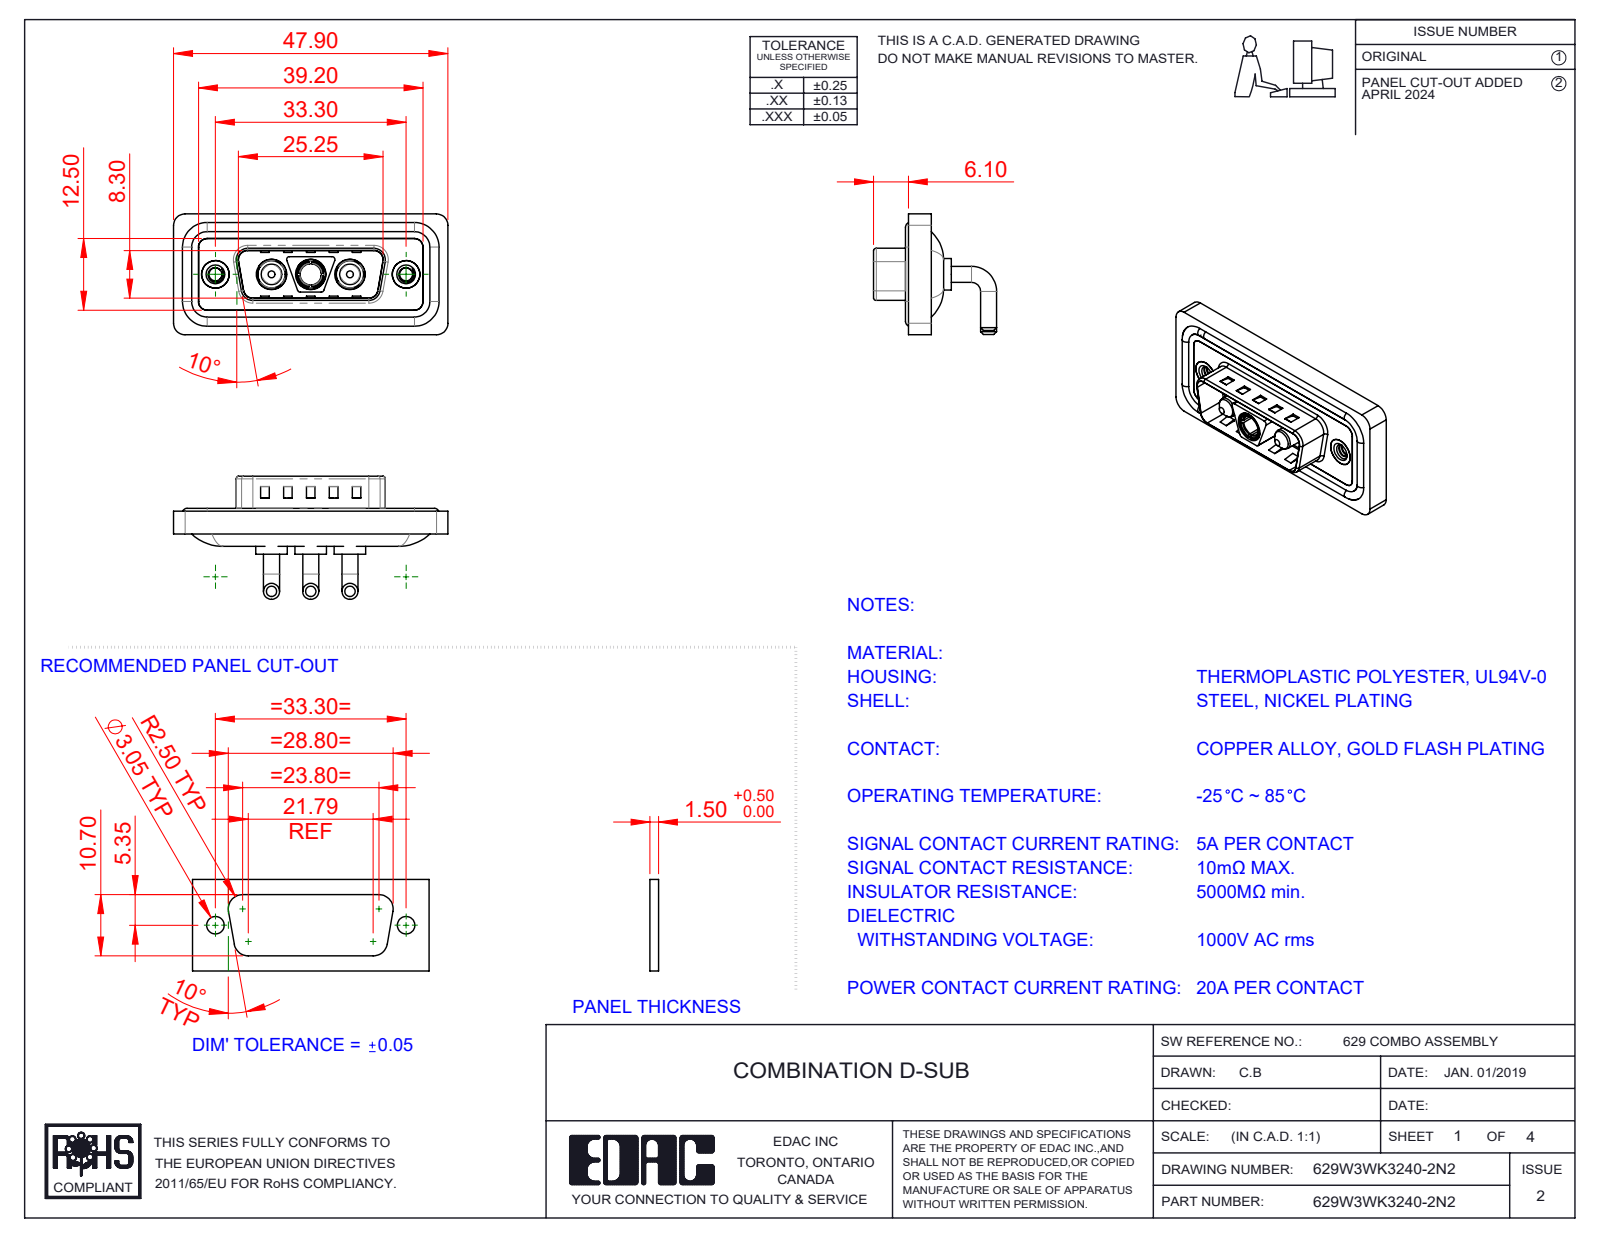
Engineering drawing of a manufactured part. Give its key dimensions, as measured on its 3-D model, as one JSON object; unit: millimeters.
{"part_name": "629Combo Waterproof Housing_15 Contacts; Power Pin_20A RA; 629Combo Threaded Rivet_2; Power Socket_20A RA (+4 more)", "step_written_by": "SolidWorks 2023 (CONFIG_CONTROL_DESIGN)", "units": "millimeters", "bodies": {"solids": 13, "faces": 621, "planar": 231, "cylindrical": 256, "other": 134}, "overall_size": [47.9, 21.5, 21.1], "volume_mm3": 5896, "surface_area_mm2": 9416, "round_holes": [[4.85, 3], [5.3, 3], [2.26, 2], [4, 2], [4.8, 2], [5, 2], [3.7, 1]], "round_bosses_or_shafts": [[2.8, 6], [1.6, 4], [5.5, 3], [5.2, 3], [4.75, 3], [3.75, 3], [4.9, 2], [3.6, 2]], "partial_cylinders_radius": [[2, 20], [1.5, 18], [0.5, 12], [1.6, 8], [0.25, 4], [0.6, 4], [0.65, 4], [0.9, 4]], "face_to_face_distances": [0.4, 2.9, 0.8, 1.1, 2.1, 1.6, 3.1, 2.5, 4.5, 3.7], "hole_center_spacings": [6.85, 9.8, 16.65, 23.5, 13.7, 33.3]}
